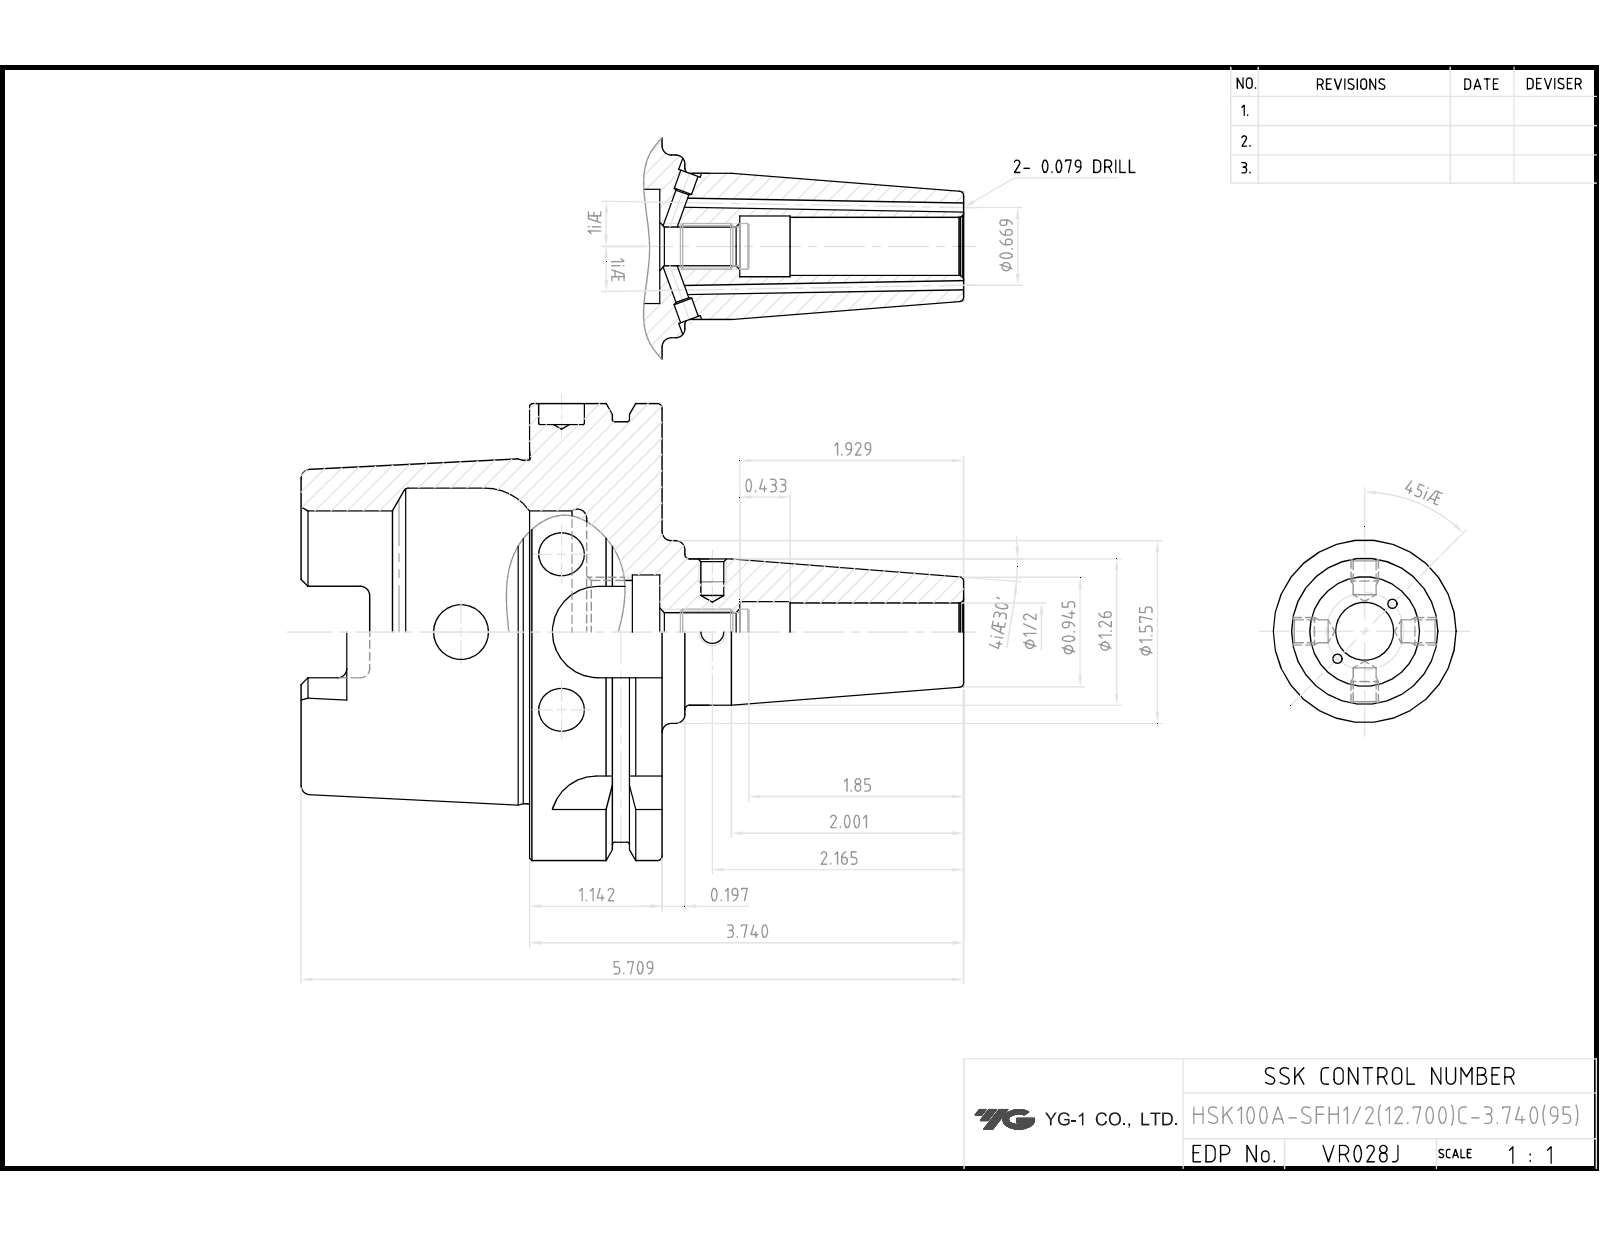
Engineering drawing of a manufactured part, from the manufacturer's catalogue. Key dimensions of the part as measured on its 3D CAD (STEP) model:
Part name (STEP PRODUCT): LO-HSK100A-SFH12.7C-95
STEP written by: Autodesk Inventor 2022 (AUTOMOTIVE_DESIGN)
Units: millimetres
Bodies: 1 solid, 121 faces (39 planar, 37 cylindrical, 45 other)
Overall size (bounding box): 145 × 100 × 100
Volume: 292 208 mm³ · Surface area: 58 366 mm²
Round holes (diameter × count): ⌀2 ×2, ⌀8.92 ×1, ⌀10 ×1, ⌀12 ×1, ⌀12.7 ×1, ⌀13.9 ×1, ⌀22.38 ×1, ⌀25 ×1, ⌀53 ×1, ⌀63 ×1
Round bosses / shafts (diameter × count): ⌀100 ×1, ⌀92 ×1, ⌀75.41 ×1, ⌀40 ×1, ⌀32 ×1
Partial cylindrical surfaces — rounded edges, fillets, slot ends (radius × count): R2 ×6, R4.88 ×4, R10 ×4
Main face-to-face distances: 29, 12.5, 16.5, 62.5, 50, 79, 28.5, 88, 78.5, 16
